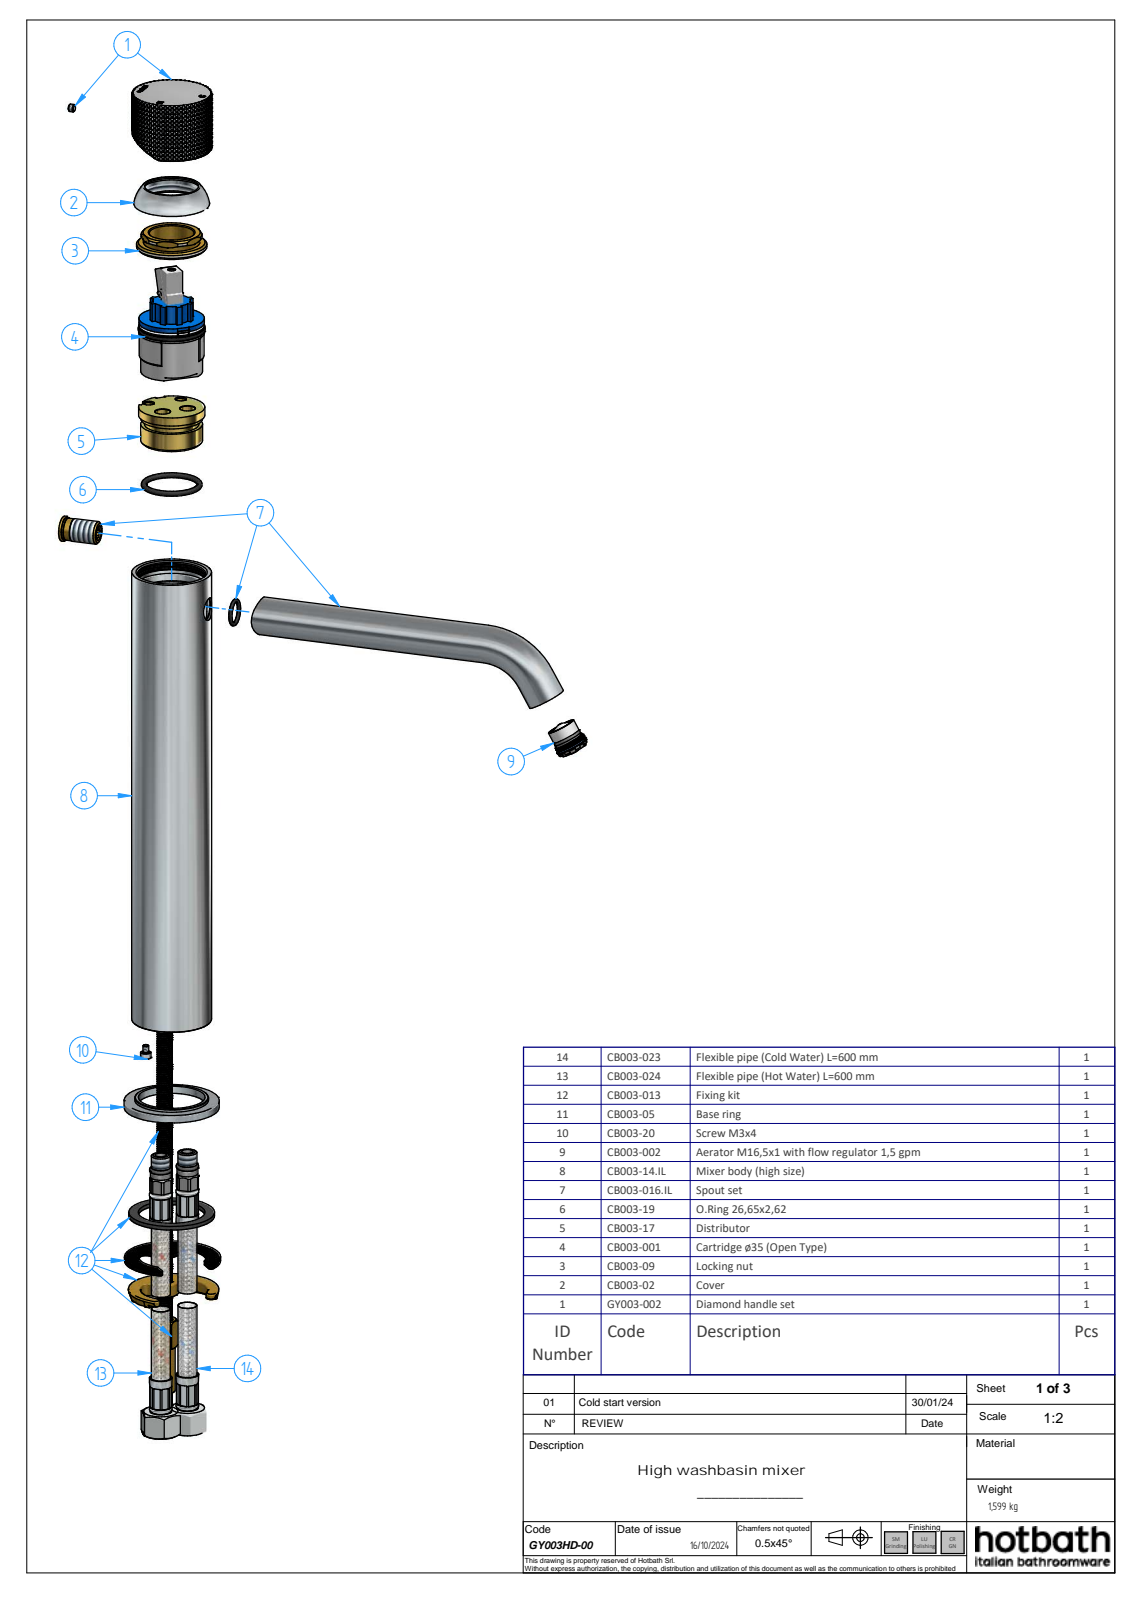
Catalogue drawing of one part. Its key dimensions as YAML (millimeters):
part_name: "GY003HD-00; CB003-14.IL; CB003-016.IL_oa_0; CB003-15.IL (+8 more)"
step_written_by: "Solid Edge (AUTOMOTIVE_DESIGN)"
units: millimeters
bodies: {solids: 9, faces: 4520, planar: 1467, cylindrical: 2631, other: 422}
overall_size: [285.5, 213.92, 50]
volume: 124859
surface_area: 101015
round_holes:
  - {diameter: 3.24, count: 1}
  - {diameter: 5, count: 1}
  - {diameter: 10.92, count: 1}
  - {diameter: 11, count: 1}
  - {diameter: 11.03, count: 1}
  - {diameter: 12, count: 1}
  - {diameter: 12.2, count: 1}
  - {diameter: 12.2, count: 1}
  - {diameter: 13.5, count: 1}
  - {diameter: 14, count: 1}
  - {diameter: 14.58, count: 1}
  - {diameter: 15.42, count: 1}
round_bosses_or_shafts:
  - {diameter: 20, count: 2}
  - {diameter: 50, count: 1}
  - {diameter: 42, count: 1}
  - {diameter: 38.7, count: 1}
  - {diameter: 18, count: 1}
  - {diameter: 16.5, count: 1}
  - {diameter: 16, count: 1}
  - {diameter: 15.42, count: 1}
partial_cylinders:
  - {radius: 0.1, count: 55}
  - {radius: 3, count: 2}
  - {radius: 0.49, count: 1}
face_to_face_distances: [279, 2.5, 281.5, 1.5, 4, 283, 253, 251.5, 249, 30]
hole_center_spacings: [34.5]
